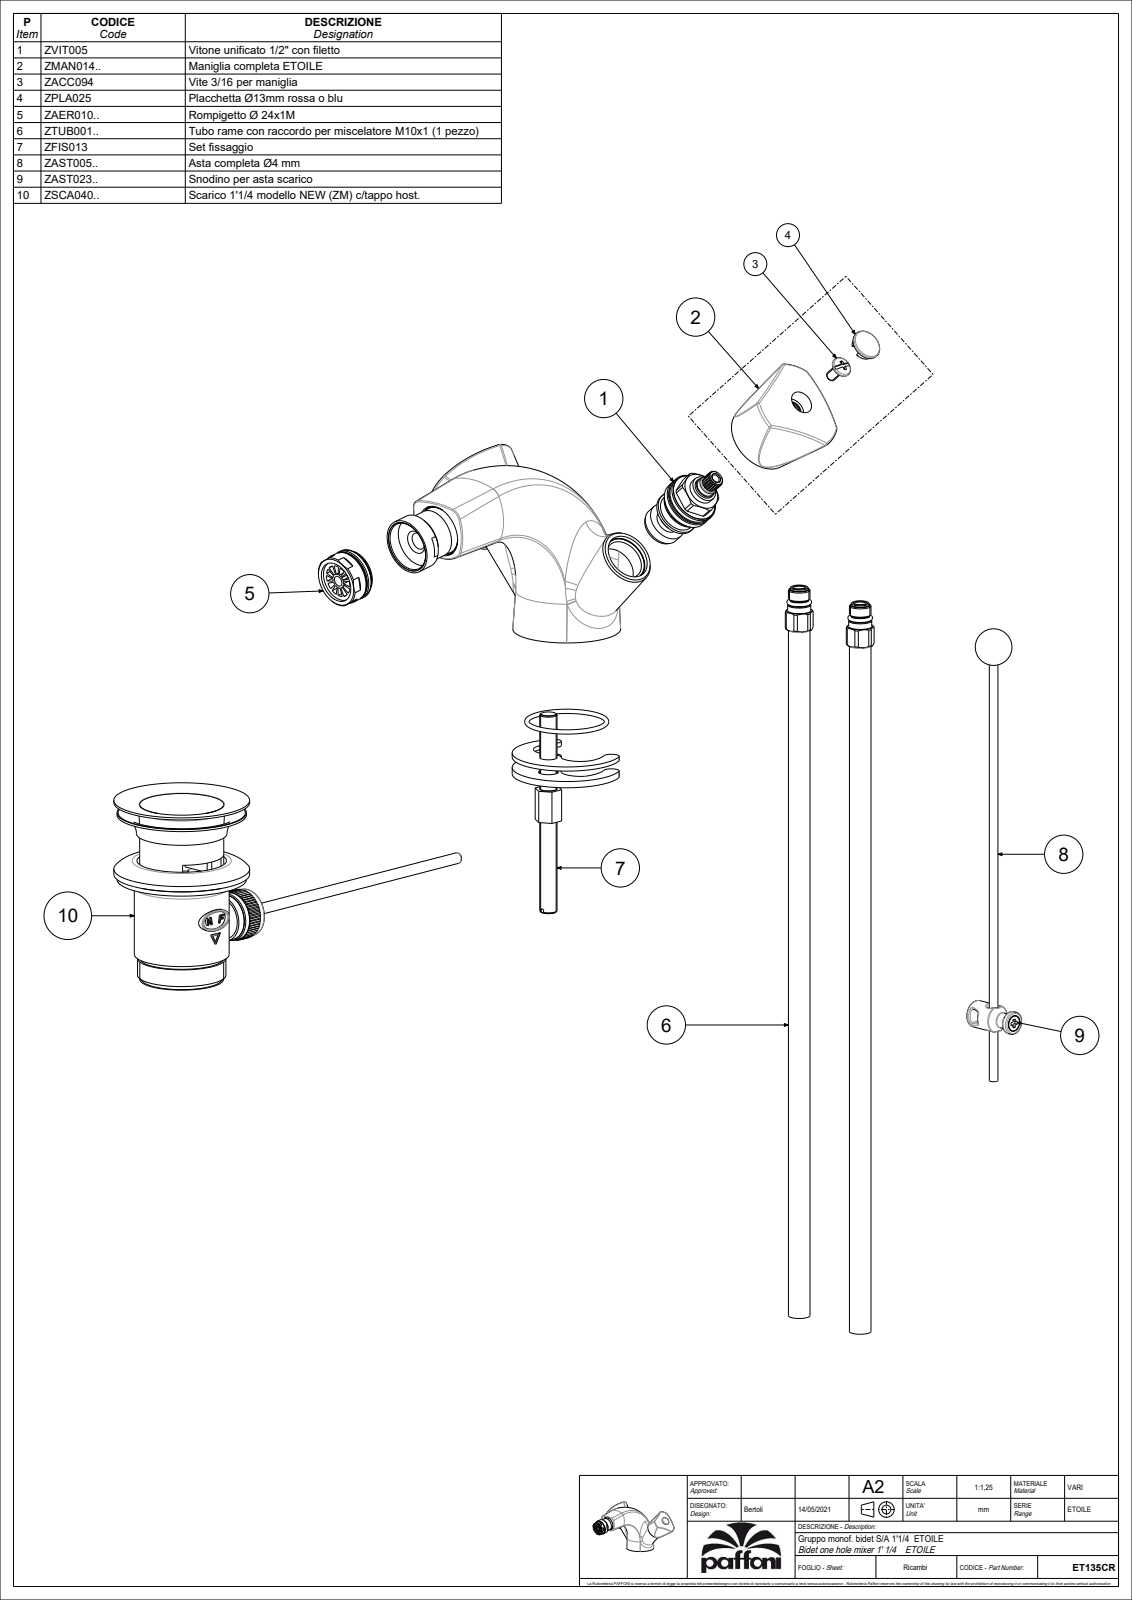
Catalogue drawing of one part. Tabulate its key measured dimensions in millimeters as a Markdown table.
| quantity | value |
| --- | --- |
| part name | ET135CR |
| STEP written by | CREO PARAMETRIC BY PTC INC, 2020044 (CONFIG_CONTROL_DESIGN) |
| units | millimeters |
| bodies | 1 solid, 568 faces (148 planar, 140 cylindrical, 280 other) |
| overall size | 154.04 × 138.85 × 85.43 |
| volume | 141 259 mm³ |
| surface area | 72 956 mm² |
| round holes (diameter × count) | 8 × 3, 19 × 3, 9 × 2, 11 × 2, 29.6 × 2, 4.8 × 1, 5 × 1, 6.8 × 1, 15 × 1, 15.5 × 1, 16 × 1, 24.5 × 1 |
| round bosses / shafts (diameter × count) | 24 × 3, 22.5 × 3, 18.6 × 2, 17.3 × 2, 14 × 2, 12.5 × 2, 11.5 × 2, 9 × 2 |
| partial cylindrical surfaces (radius × count) | 1 × 4, 3 × 2, 5 × 2, 8 × 2, 10 × 2, 13 × 2, 13.5 × 2, 3.4 × 1 |
| main face-to-face distances | 6, 23, 40.81, 11, 1.5, 29, 3, 9, 15, 12 |
| hole center spacings | 7.5, 12.5, 14.15, 10, 12, 15, 22 |
